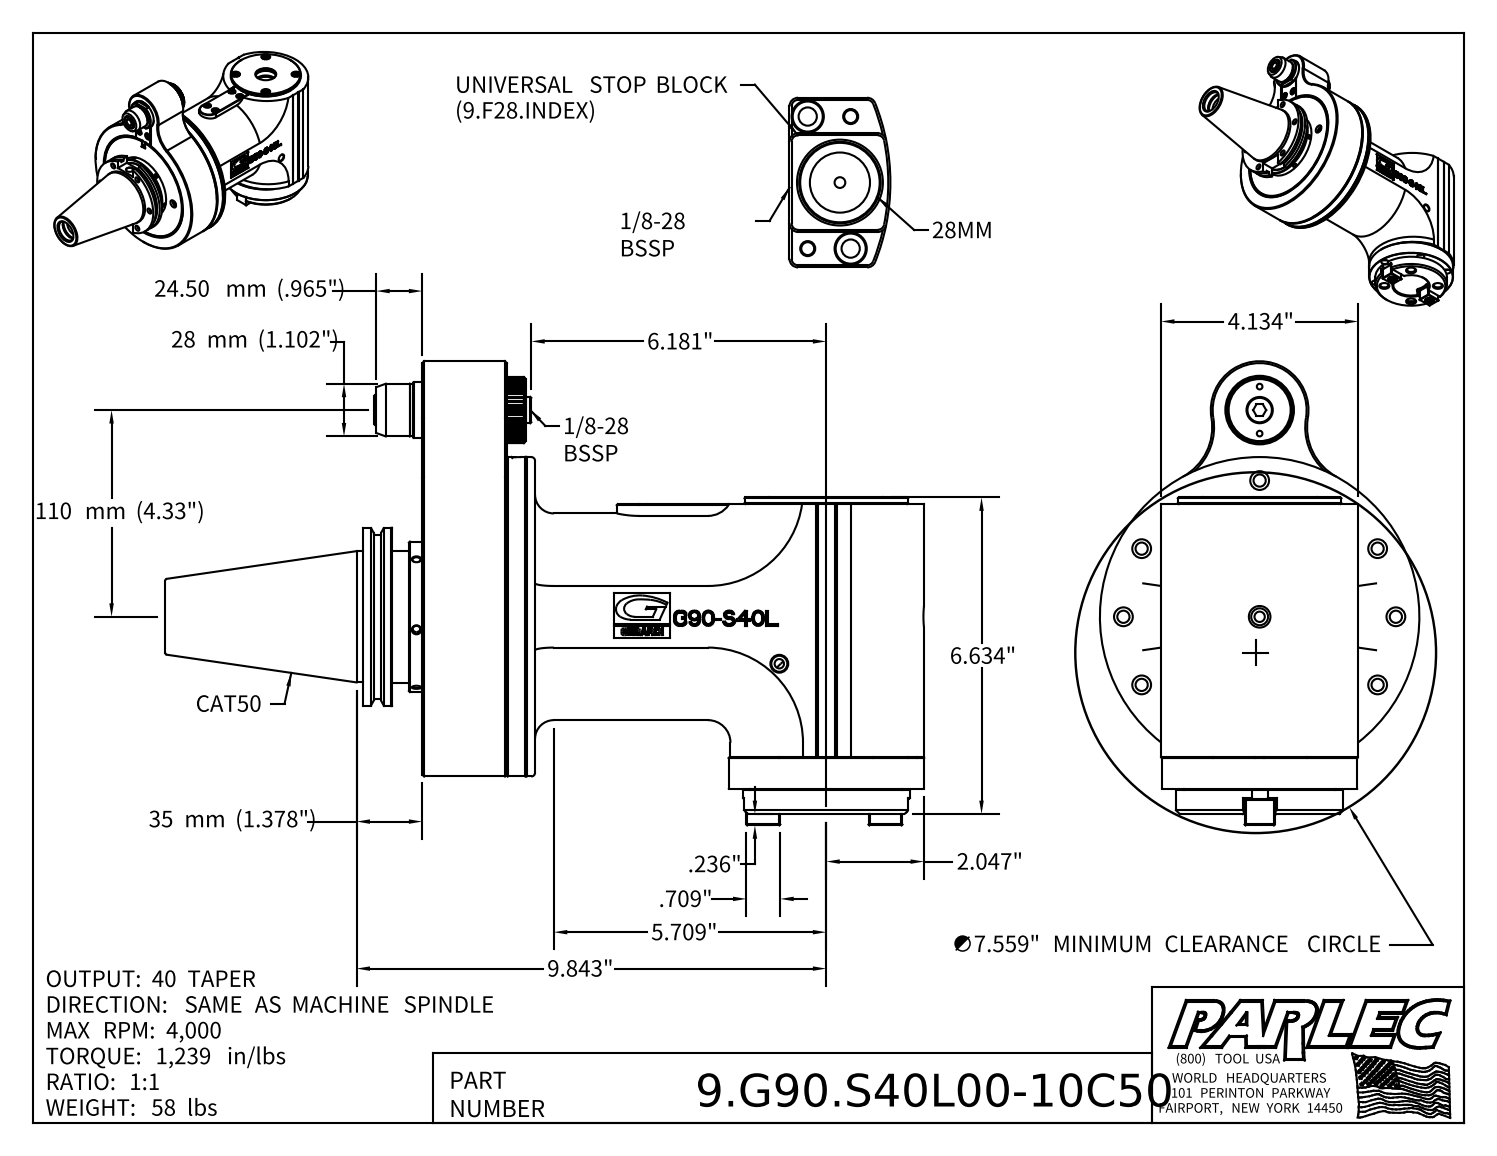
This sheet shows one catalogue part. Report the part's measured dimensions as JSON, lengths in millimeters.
{"part_name": "9.G90.S40L00-10C50; 9_G90_S40L0-250; 9_GA4_451_1 (Classic, Type 4, Cat50, 110mm, 28x24.5P)", "step_written_by": "Autodesk Inventor 2022 (AUTOMOTIVE_DESIGN)", "units": "millimeters", "bodies": {"solids": 3, "faces": 1803, "planar": 982, "cylindrical": 377, "other": 444}, "overall_size": [403.8, 247, 170], "volume_mm3": 4120000, "surface_area_mm2": 476300, "round_holes": [[4.2, 21], [9, 15], [6.5, 13], [10, 13], [5.5, 7], [3.3, 6], [5, 6], [8.5, 5], [8, 4], [3, 2], [5.2, 2], [10.5, 2]], "round_bosses_or_shafts": [[8, 9], [7, 4], [35, 2], [10, 2], [7.8, 2], [5, 2], [170, 1], [160, 1]], "partial_cylinders_radius": [[3, 16], [1, 12], [10, 6], [2.1, 4], [4.5, 2], [5, 2], [10, 2], [12, 2]], "face_to_face_distances": [45, 15, 5.7, 39.3, 17, 60, 105, 54.3, 30, 1.8], "hole_center_spacings": [72.5, 52.5, 40.2, 20.5, 37.5, 46, 58.3, 87.3]}
